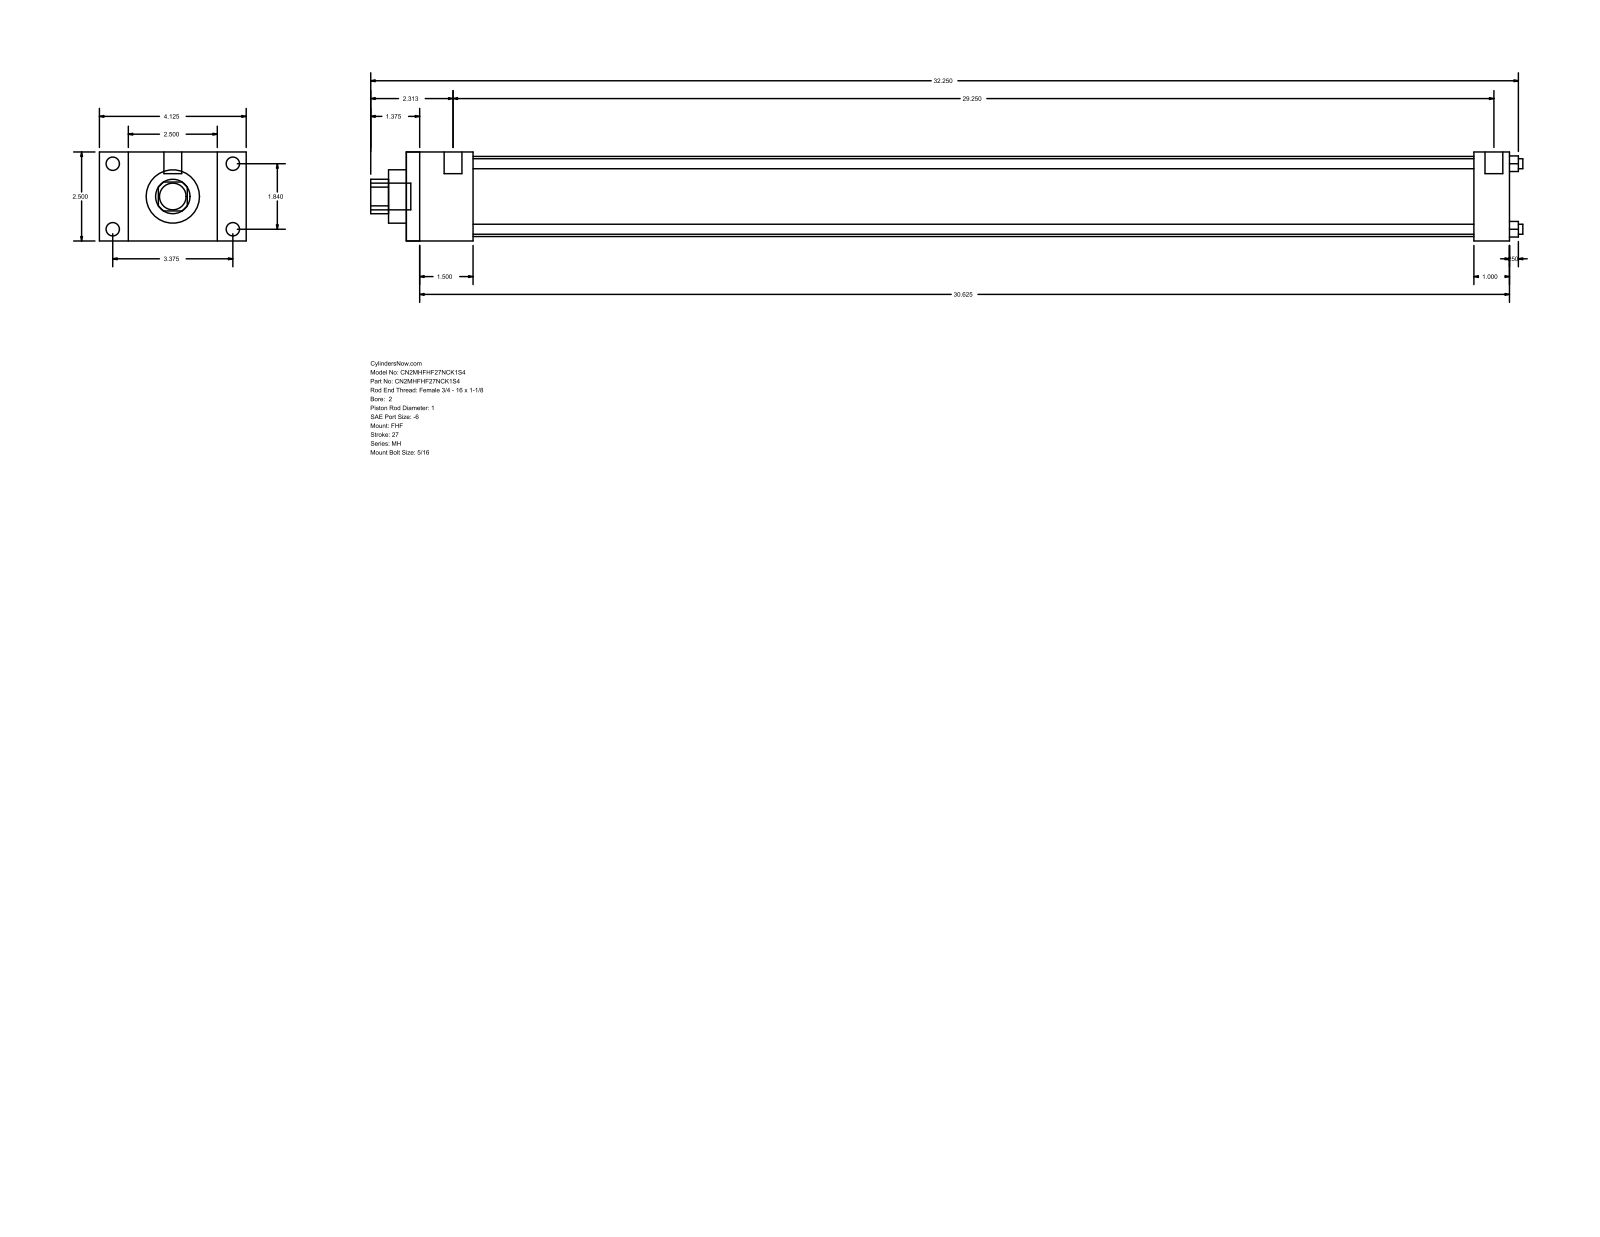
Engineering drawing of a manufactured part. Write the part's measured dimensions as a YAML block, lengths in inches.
part_name: "MH_FHF__0200_1"
step_written_by: "GSSL Pune (CONFIG_CONTROL_DESIGN)"
units: inches
bodies: {solids: 0, faces: 88, planar: 60, cylindrical: 28, other: 0}
overall_size: [32.375, 4.125, 2.5]
round_holes:
  - {diameter: 0.281, count: 4}
  - {diameter: 1, count: 1}
  - {diameter: 1.5, count: 1}
  - {diameter: 2.25, count: 1}
round_bosses_or_shafts:
  - {diameter: 0.375, count: 4}
  - {diameter: 0.219, count: 4}
  - {diameter: 0.5, count: 2}
  - {diameter: 0.75, count: 1}
partial_cylinders:
  - {radius: 0.484, count: 1}
face_to_face_distances: [2.5, 31, 1.875, 29.125, 0.813, 3.313, 4.125, 1, 30, 28.125]
hole_center_spacings: [1.301, 1.84, 2.602]
